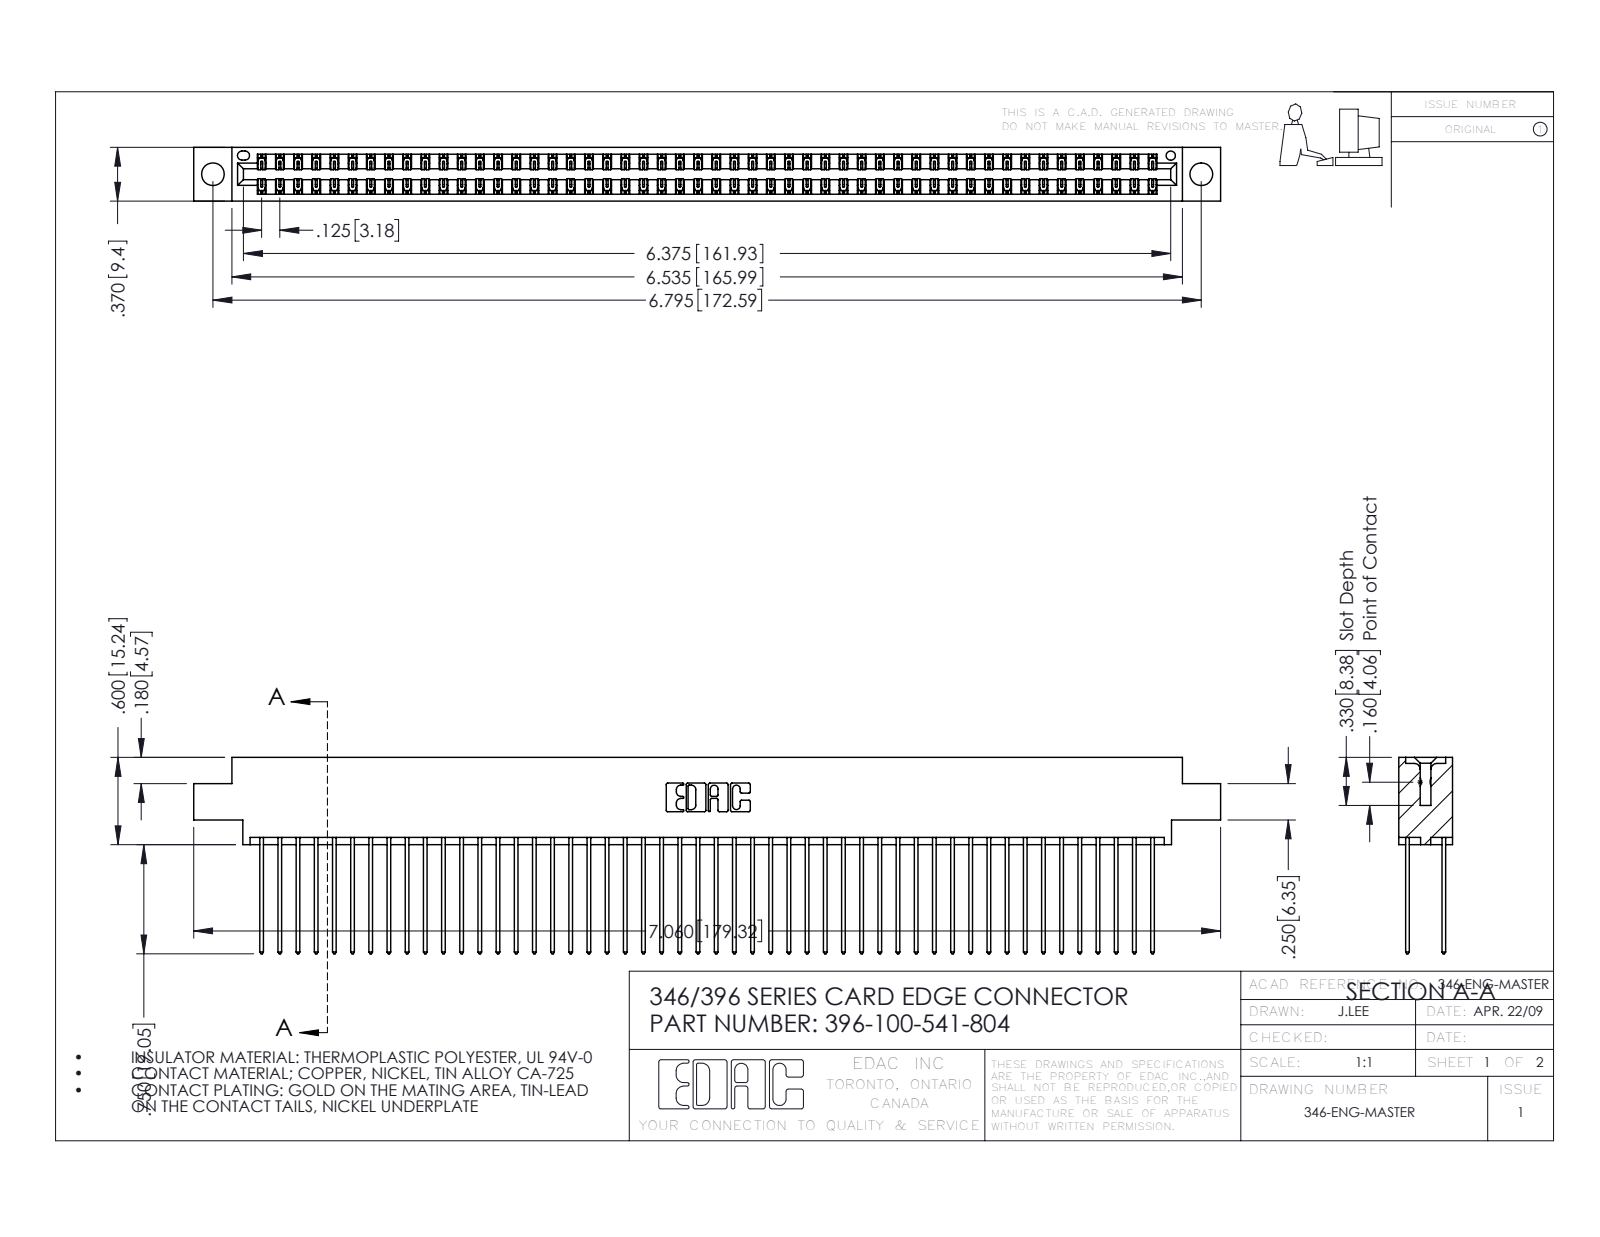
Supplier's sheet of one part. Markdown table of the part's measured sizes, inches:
| quantity | value |
| --- | --- |
| part name | 345-292-001_345-293-141; 396-100-541-804; 346 Part_0.170 Offset - 0.156 Dia-TH |
| STEP written by | SolidWorks 2016 (CONFIG_CONTROL_DESIGN) |
| units | inches |
| bodies | 101 solids, 5326 faces (3580 planar, 1746 cylindrical, 0 other) |
| overall size | 7.06 × 1.35 × 0.37 |
| volume | 1.091 in³ |
| surface area | 42.54 in² |
| round holes (diameter × count) | 0.156 × 2, 0.064 × 1 |
| partial cylindrical surfaces (radius × count) | 0.006 × 150, 0.01 × 100, 0.01 × 22, 0.007 × 6, 0.031 × 6, 0.026 × 3, 0.014 × 2, 0.022 × 2 |
| main face-to-face distances | 0.048, 0.322, 0.25, 0.072, 0.298, 0.025, 0.37, 0.275, 0.225, 0.148 |
| hole center spacings | 0.246, 6.586, 6.795 |
